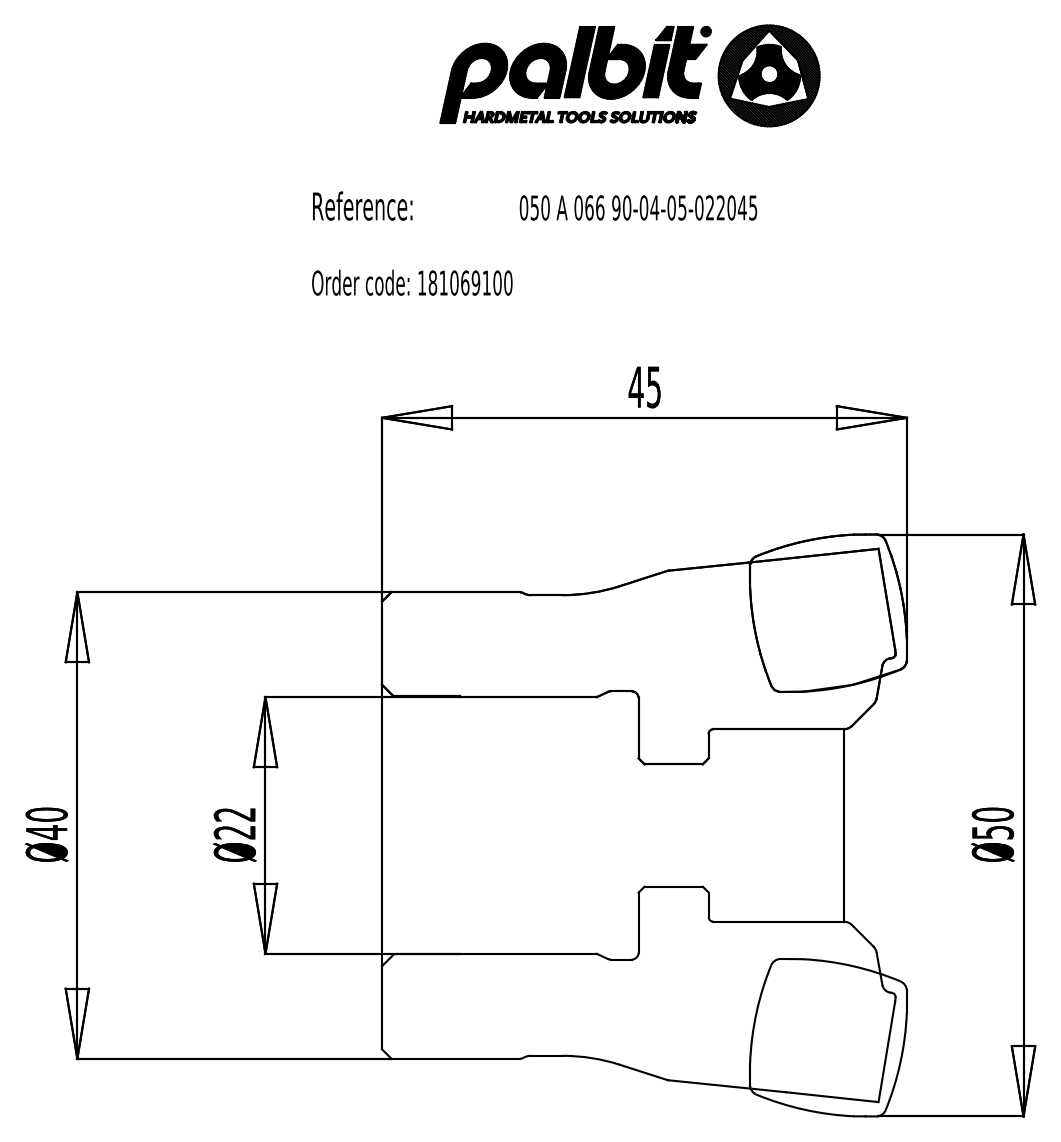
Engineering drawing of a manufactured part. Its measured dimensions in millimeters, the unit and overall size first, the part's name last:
Units: millimetres
Overall size (bounding box): 49.9 × 49.9 × 44.99
Round holes (diameter × count): ⌀10.5 ×1, ⌀16.5 ×1, ⌀22 ×1, ⌀22.12 ×1, ⌀23 ×1
Round bosses / shafts (diameter × count): ⌀40 ×1, ⌀39.5 ×1
Main face-to-face distances: 22, 9.55, 31.55, 13.44, 22.99, 44.99, 16.99, 3.55, 6, 28
Volume: 66 838 mm³ · Surface area: 16 257 mm²
Bodies: 2 solids, 57 faces (6 planar, 7 cylindrical, 44 other)
Part name (STEP PRODUCT): NOCUT^CUT PROFILE - 181069100; CUT^CUT PROFILE - 181069100; CUT PROFILE - 181069100
STEP written by: SolidWorks 2015 (CONFIG_CONTROL_DESIGN)
